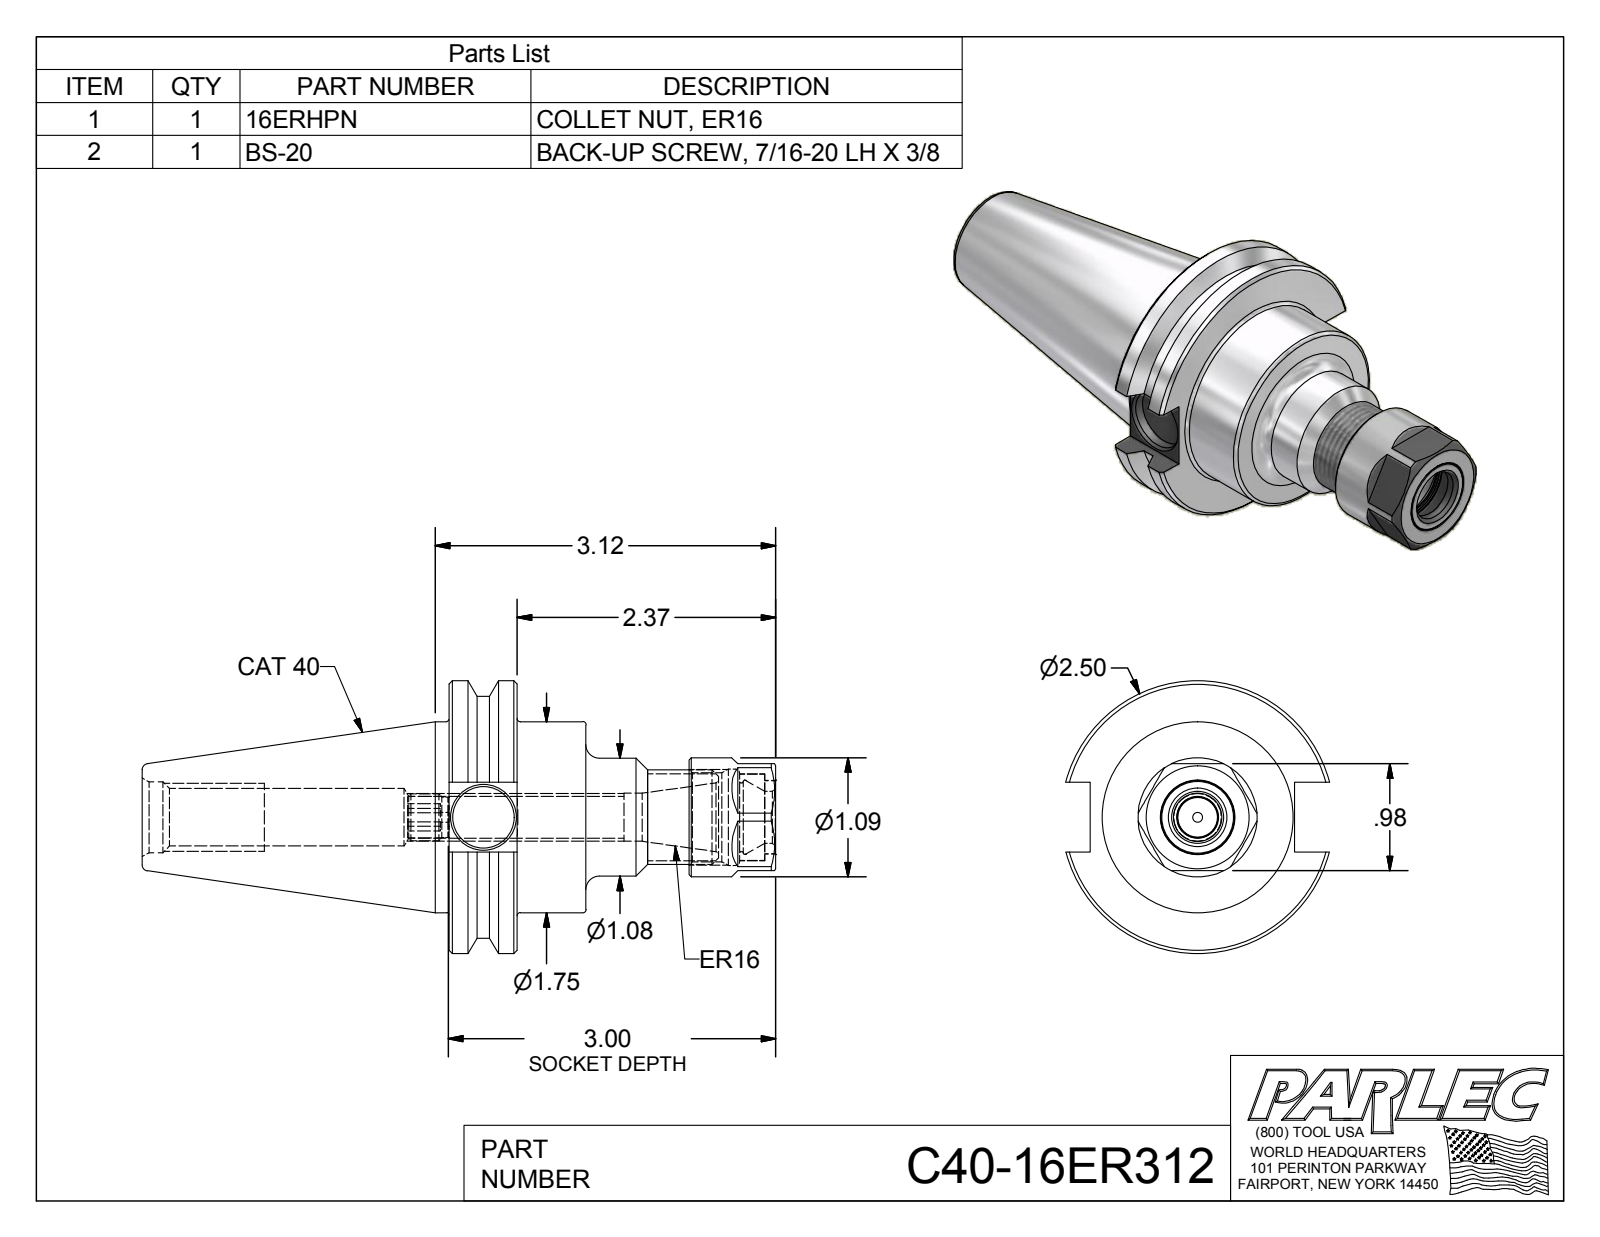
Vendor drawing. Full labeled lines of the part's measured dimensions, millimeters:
Part name (STEP PRODUCT): C40-16ER312; C40-16ER3-1; 16ERHPN; BS-20
STEP written by: Autodesk Inventor 2012 (AUTOMOTIVE_DESIGN)
Units: millimetres
Bodies: 4 solids, 108 faces (41 planar, 28 cylindrical, 39 other)
Overall size (bounding box): 147.5 × 63.5 × 61.4
Volume: 143 400 mm³ · Surface area: 31 120 mm²
Round holes (diameter × count): ⌀2.3 ×1, ⌀9.7 ×1, ⌀11.2 ×1, ⌀12 ×1, ⌀13.4 ×1, ⌀14.3 ×1, ⌀16 ×1, ⌀16.5 ×1, ⌀17.1 ×1, ⌀17.3 ×1, ⌀20.2 ×1, ⌀20.7 ×1
Round bosses / shafts (diameter × count): ⌀63.5 ×1, ⌀56.4 ×1, ⌀44.5 ×1, ⌀27.7 ×1, ⌀27.4 ×1, ⌀22 ×1, ⌀20.1 ×1, ⌀17 ×1
Main face-to-face distances: 15.9, 16, 31.9, 24.9, 76.1, 60.2, 44.2, 4.3, 20.6, 16.3
